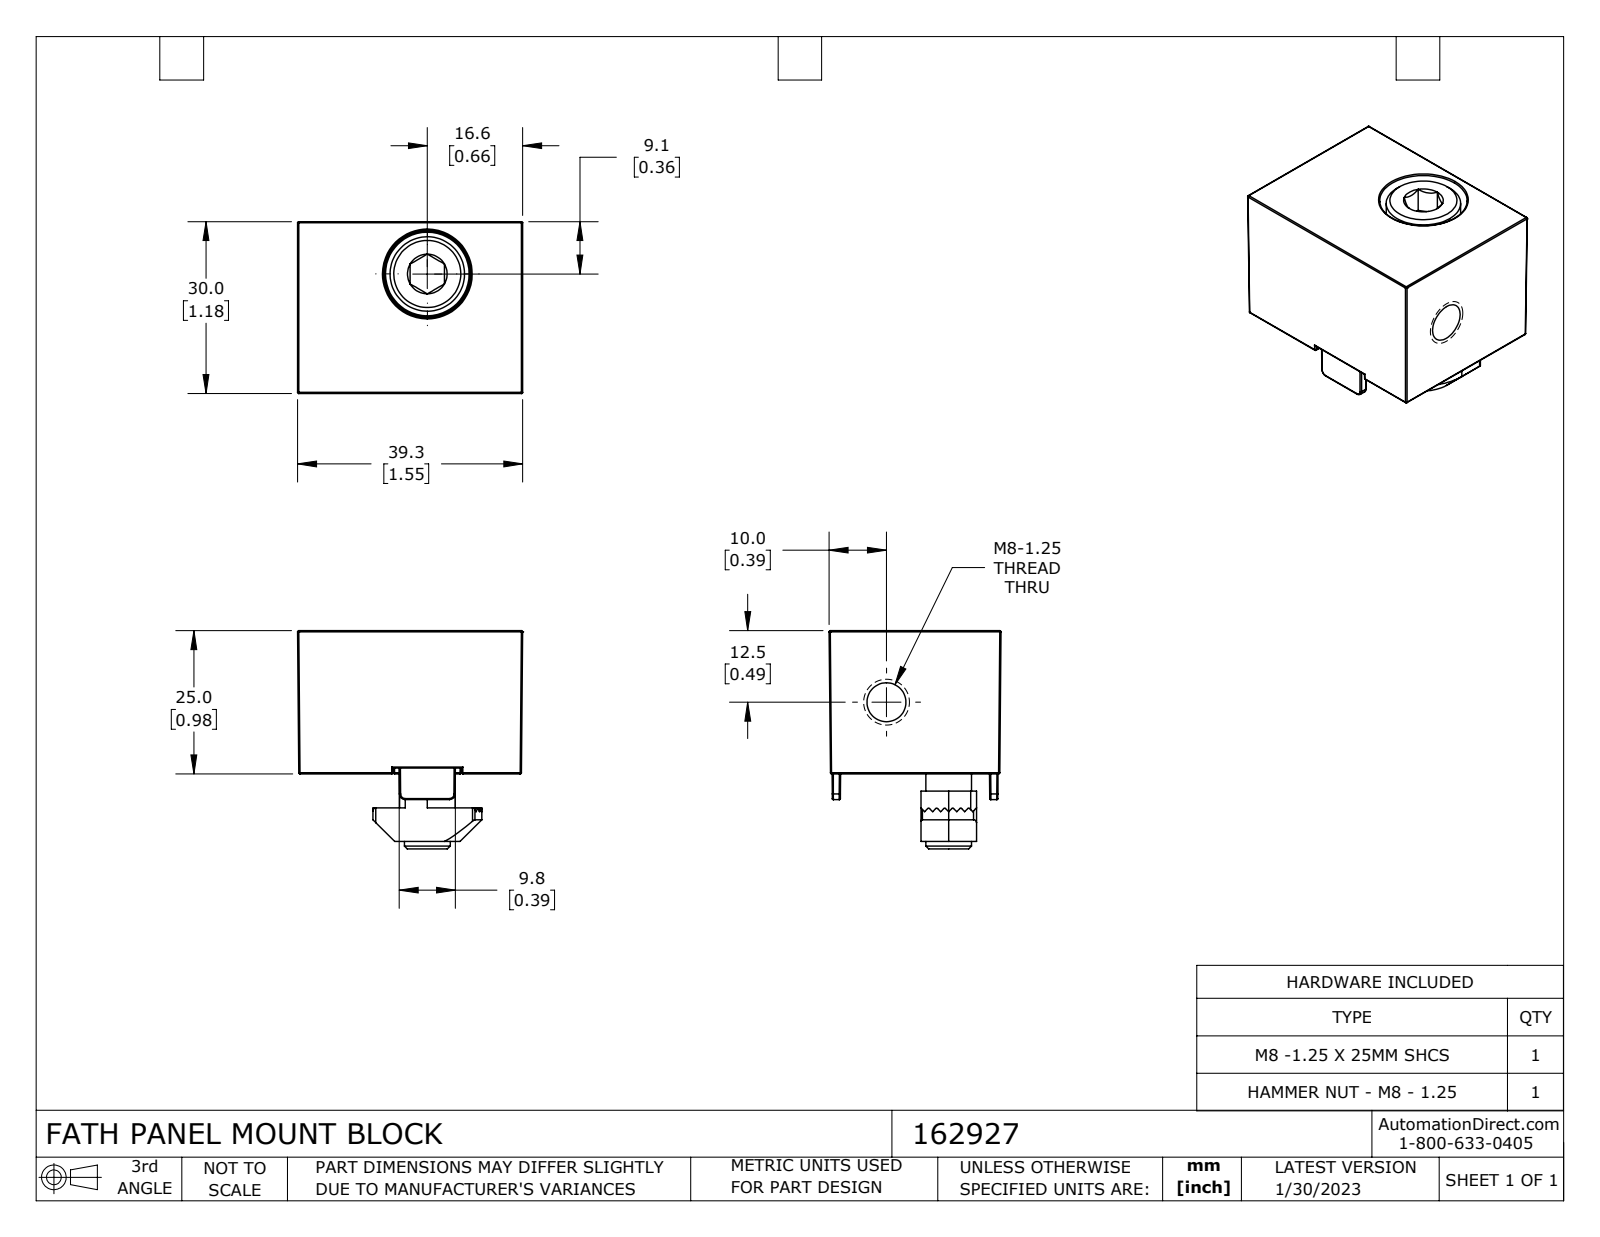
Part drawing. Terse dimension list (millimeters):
name: 162927
written by: SolidWorks 2021 (CONFIG_CONTROL_DESIGN)
unit: mm
bodies: 2 solids, 341 faces (96 planar, 129 cylindrical, 116 other)
size: 39.3 × 38.1 × 30
volume: 20 960 mm³; area: 11 630 mm²
holes: 2× ⌀6.8
bosses: 1× ⌀13, 1× ⌀8
rounds: 75× R0.2, 10× R0.5, 4× R1, 1× R4.9, 1× R5.4, 1× R9.5
face distances: 25, 10.1, 26.5, 20.5, 14.9, 3, 12.8, 9.7, 27.5, 1
